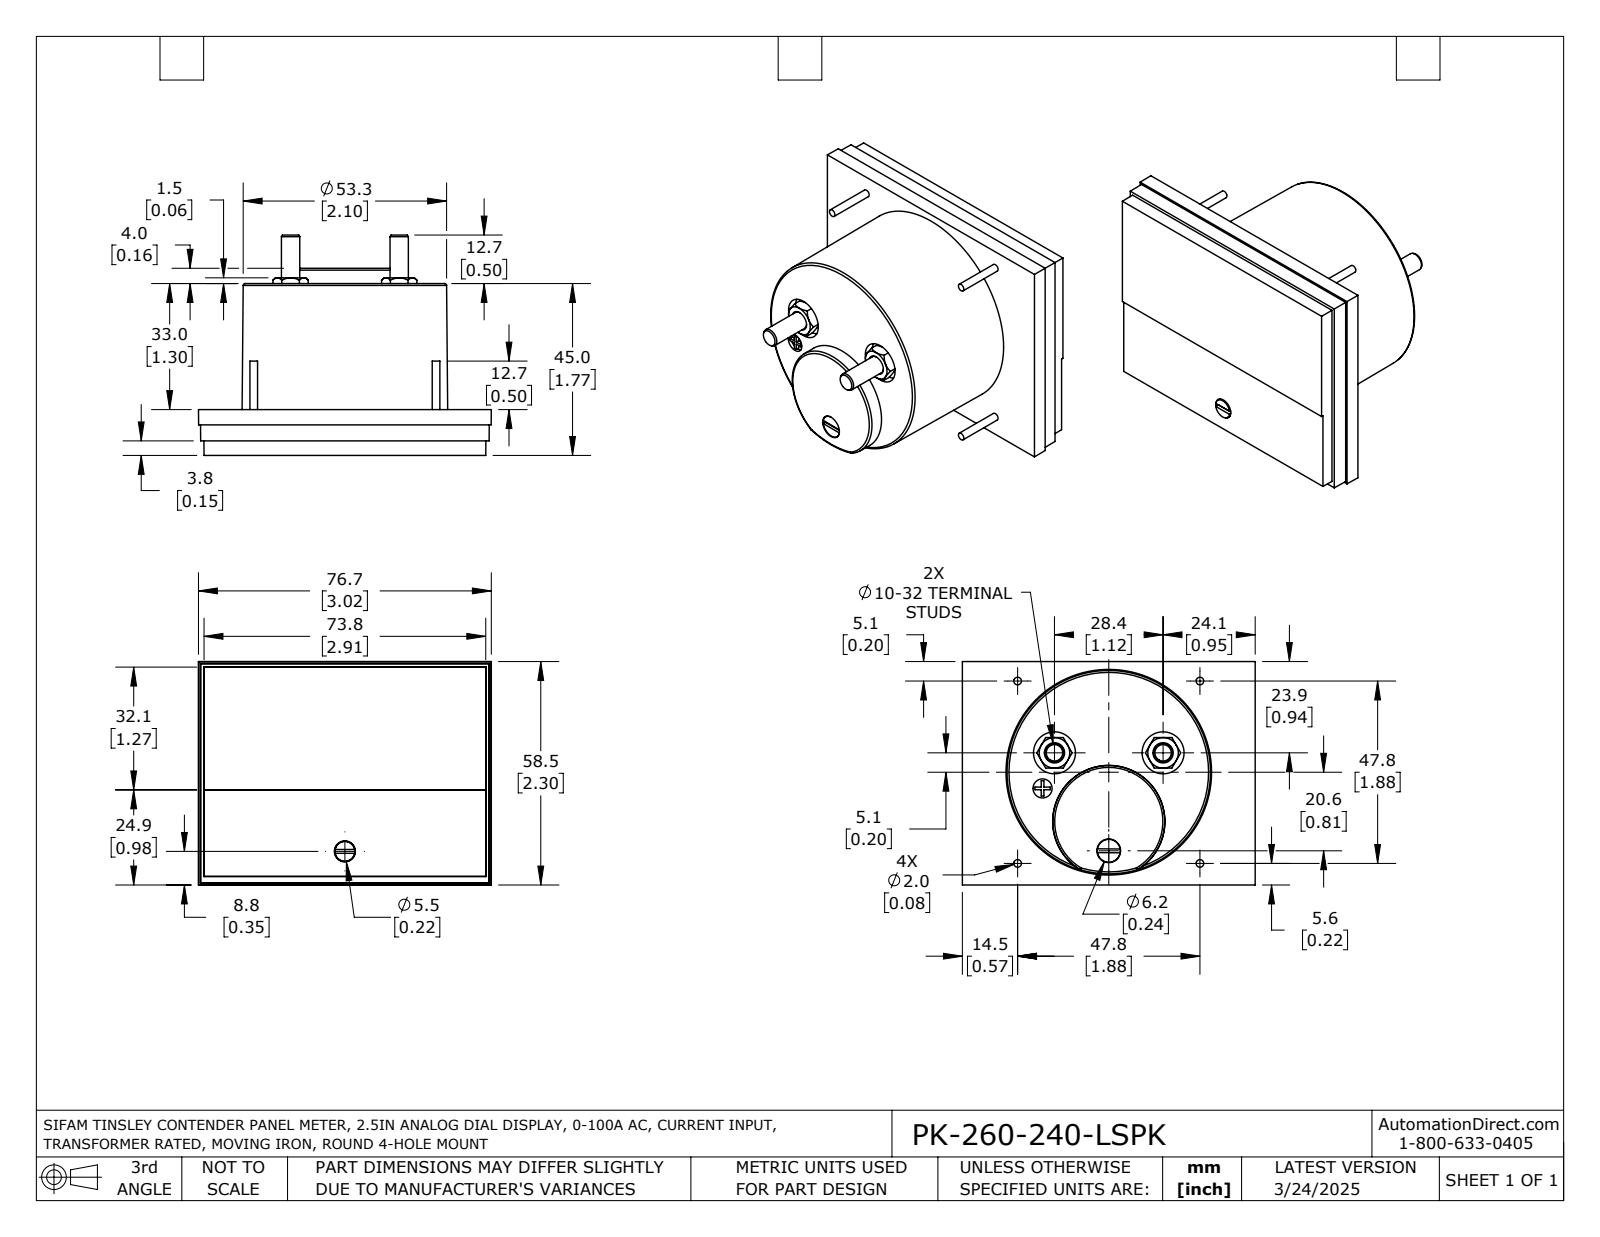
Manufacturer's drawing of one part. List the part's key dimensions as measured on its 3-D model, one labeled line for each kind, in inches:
Part name (STEP PRODUCT): PK-260-240-LSPK
STEP written by: SolidWorks 2021 (AUTOMOTIVE_DESIGN)
Units: inches
Bodies: 1 solid, 192 faces (95 planar, 37 cylindrical, 60 other)
Overall size (bounding box): 3.02 × 2.303 × 2.272
Volume: 7.657 in³ · Surface area: 36.55 in²
Round holes (diameter × count): ⌀0.197 ×3, ⌀0.433 ×2, ⌀0.209 ×1, ⌀0.217 ×1, ⌀0.244 ×1
Round bosses / shafts (diameter × count): ⌀0.079 ×4, ⌀0.189 ×2, ⌀0.236 ×1, ⌀0.205 ×1
Partial cylindrical surfaces — rounded edges, fillets, slot ends (radius × count): R0.033 ×1
Main face-to-face distances: 0.02, 0.472, 0.13, 0.322, 0.15, 0.453, 0.057, 0.077, 0.396, 0.073
Hole centre spacings: 1.155, 1.16, 0.387, 0.938, 0.942, 1.12, 1.295
